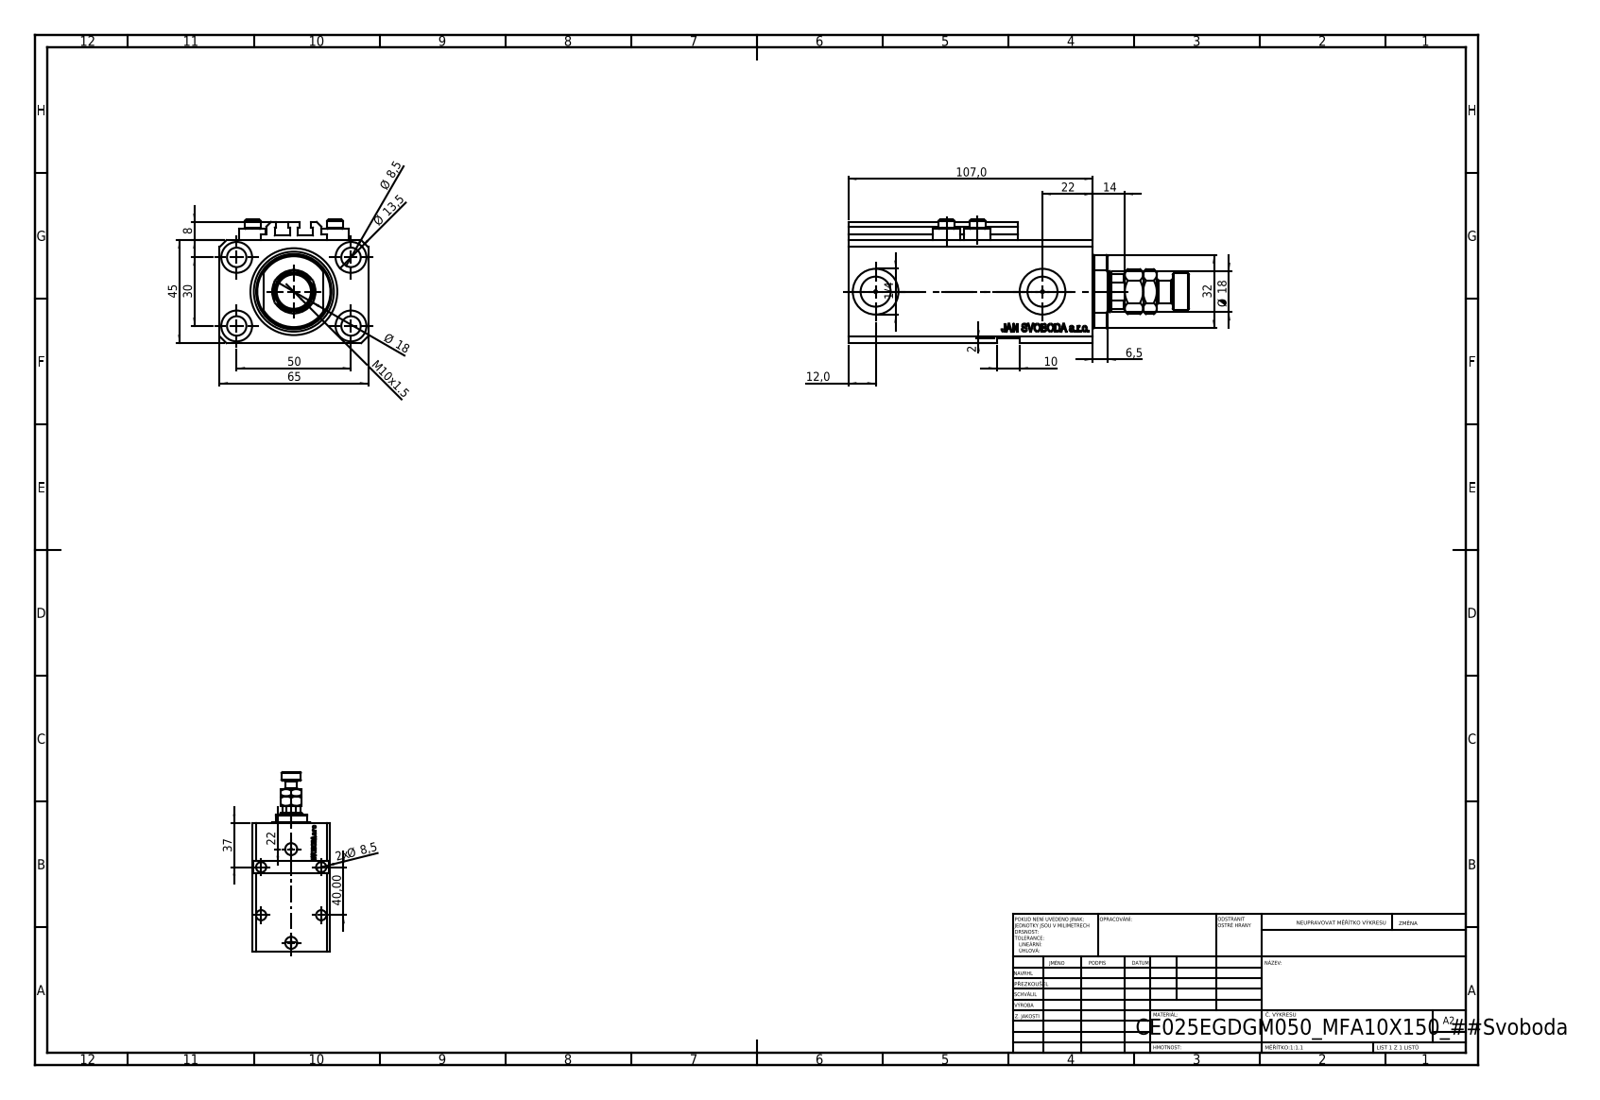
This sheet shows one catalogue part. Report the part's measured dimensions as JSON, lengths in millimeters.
{"part_name": "V250CE_C_VCP; V250CE_VC_E; MFA; ALLEN BOLT V250CE (+1 more)", "step_written_by": "SolidWorks 2019 (CONFIG_CONTROL_DESIGN)", "units": "millimeters", "bodies": {"solids": 9, "faces": 1155, "planar": 531, "cylindrical": 162, "other": 462}, "overall_size": [149, 65, 54], "volume_mm3": 275209, "surface_area_mm2": 80077, "round_holes": [[8.5, 9], [1.25, 4], [4, 4], [13.5, 4], [10, 2], [13.16, 2], [20, 2], [18, 1], [25, 1], [38, 1]], "round_bosses_or_shafts": [[11.6, 4], [7, 4], [16, 1], [10, 1]], "partial_cylinders_radius": [[0.2, 10], [8.5, 1], [16, 1]], "face_to_face_distances": [45, 65, 14, 93, 2, 47, 107, 6.9, 20.5, 24], "hole_center_spacings": [29.15, 50, 13.6, 14.76, 15.12, 27.51, 27.89, 30]}
